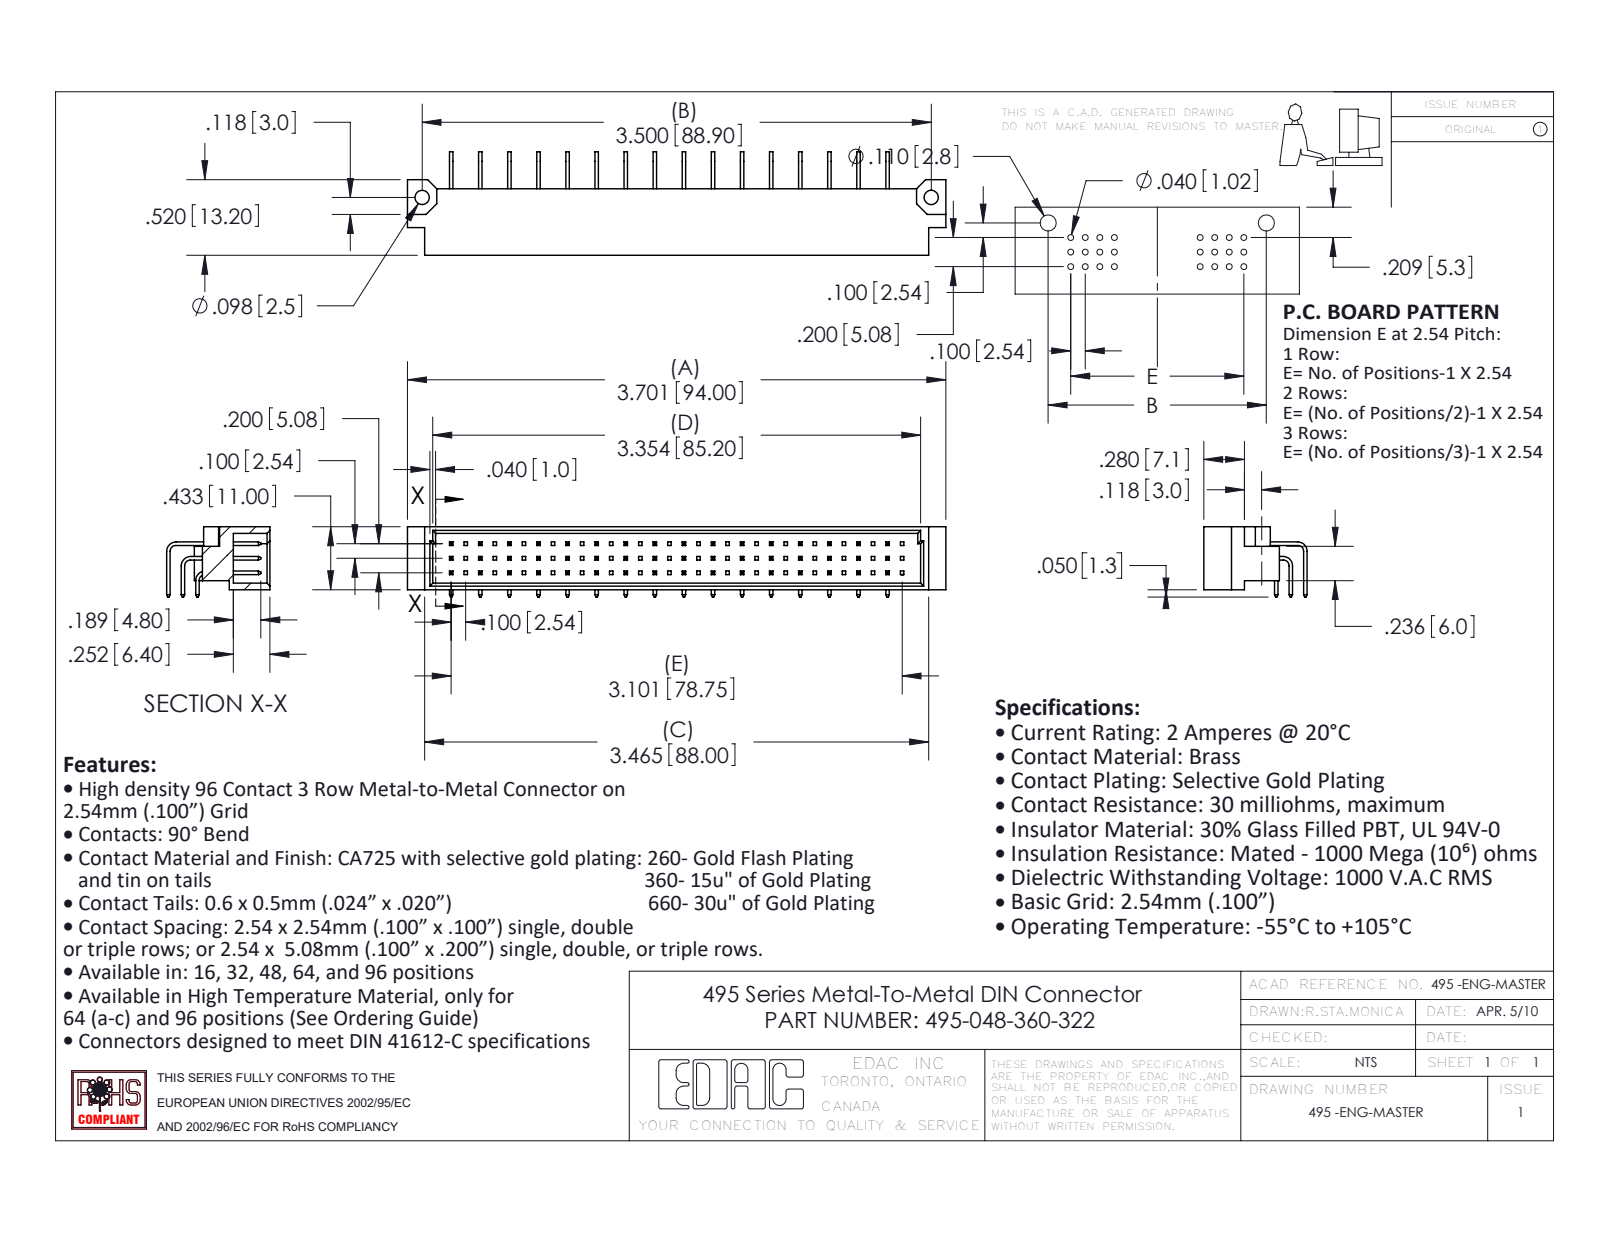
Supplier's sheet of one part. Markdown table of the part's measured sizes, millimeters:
| quantity | value |
| --- | --- |
| part name | 495-048-360-322; 495-290-2; 495-290-3; 495 Part_96 (+1 more) |
| STEP written by | SolidWorks 2020 (AUTOMOTIVE_DESIGN) |
| units | millimeters |
| bodies | 49 solids, 1297 faces (1197 planar, 100 cylindrical, 0 other) |
| overall size | 94 × 18.05 × 12.27 |
| volume | 6 276 mm³ |
| surface area | 9 144 mm² |
| round holes (diameter × count) | 2.49 × 2 |
| partial cylindrical surfaces (radius × count) | 1.02 × 3, 1.65 × 3 |
| main face-to-face distances | 5.08, 1.14, 9.86, 2.54, 5.2, 0.61, 11, 10.16, 15.24, 20.32 |
| hole center spacings | 88.9 |
